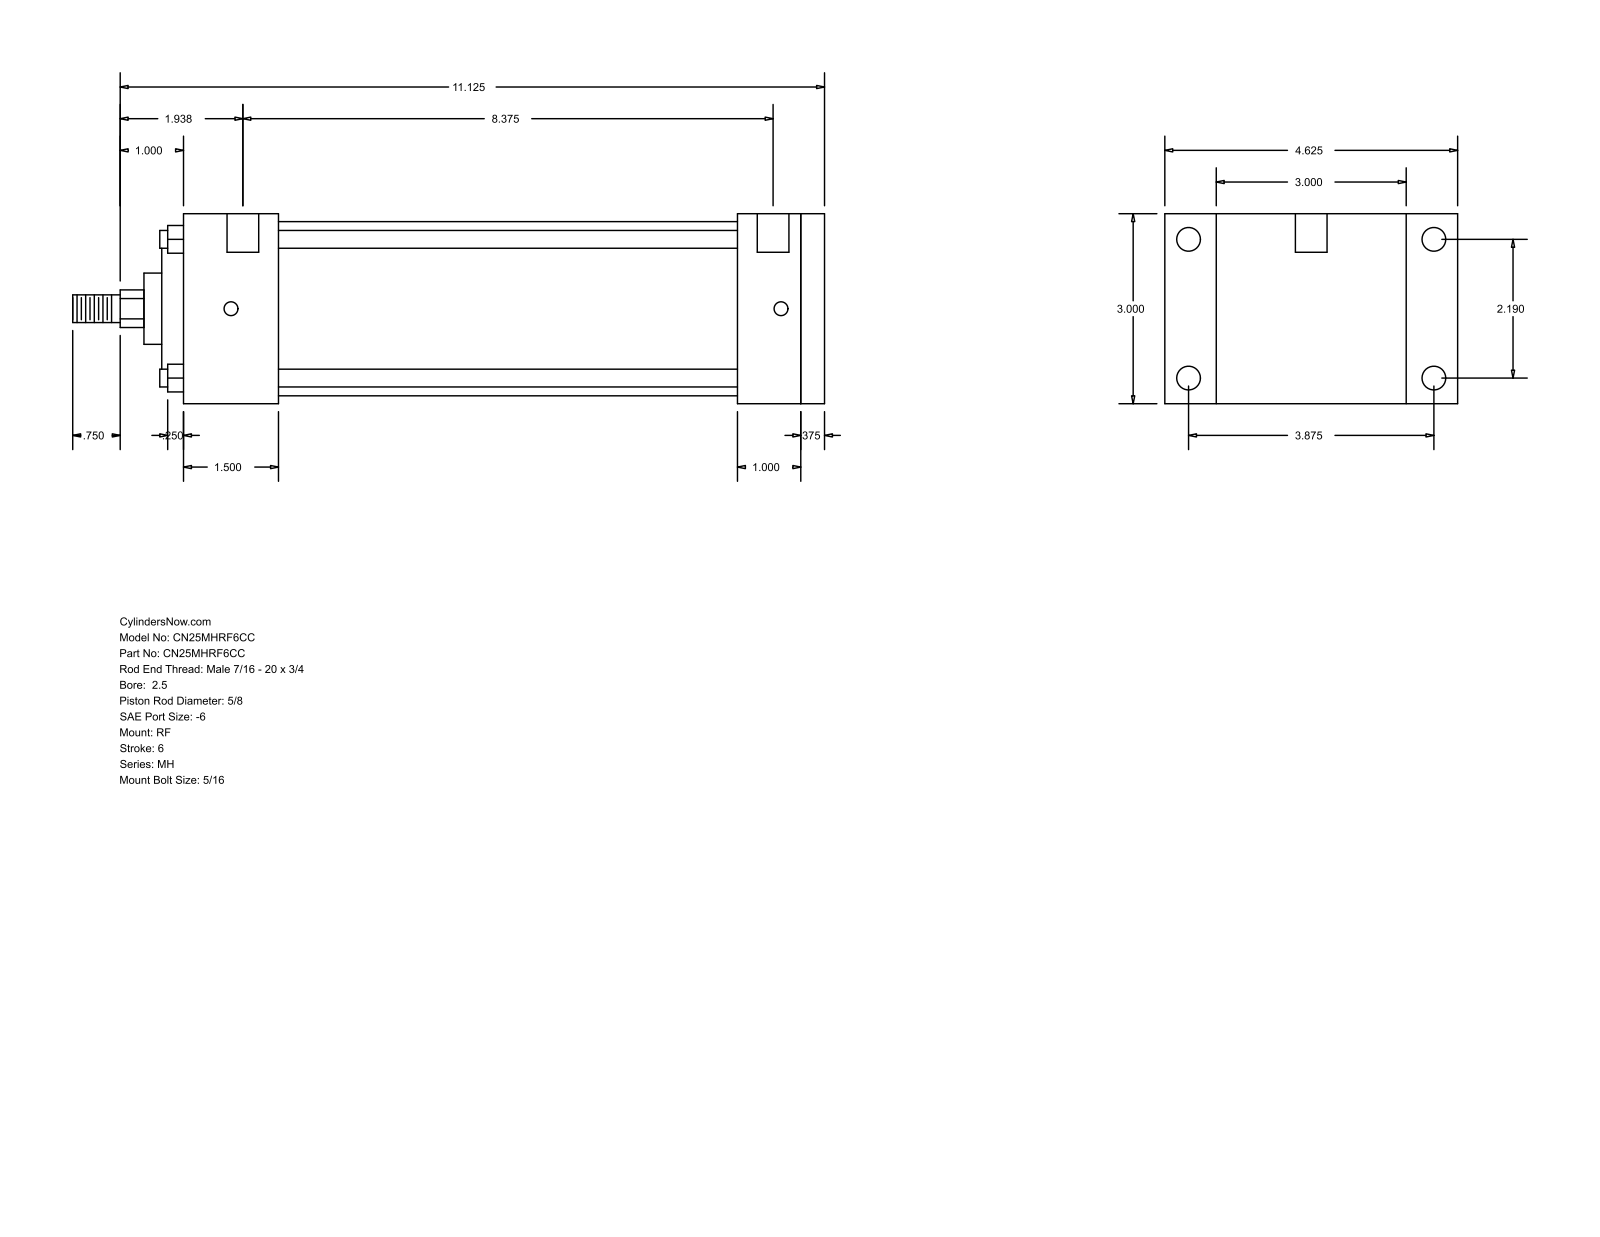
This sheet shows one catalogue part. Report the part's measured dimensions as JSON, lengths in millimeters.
{"part_name": "MH_RF__0250_0.625", "step_written_by": "GSSL Pune (CONFIG_CONTROL_DESIGN)", "units": "millimeters", "bodies": {"solids": 0, "faces": 94, "planar": 65, "cylindrical": 29, "other": 0}, "overall_size": [301.62, 117.47, 76.2], "round_holes": [[5.56, 4], [9.53, 4], [12.7, 2]], "round_bosses_or_shafts": [[7.14, 4], [69.85, 1], [55.55, 1], [28.57, 1], [15.88, 1], [11.11, 1]], "partial_cylinders_radius": [[7.54, 1]], "face_to_face_distances": [76.2, 9.52, 257.17, 247.65, 25.4, 38.1, 222.25, 34.92, 184.15, 209.55], "hole_center_spacings": [55.62, 98.42, 113.05, 220.66, 3.17, 4.76, 212.73, 215.9]}
